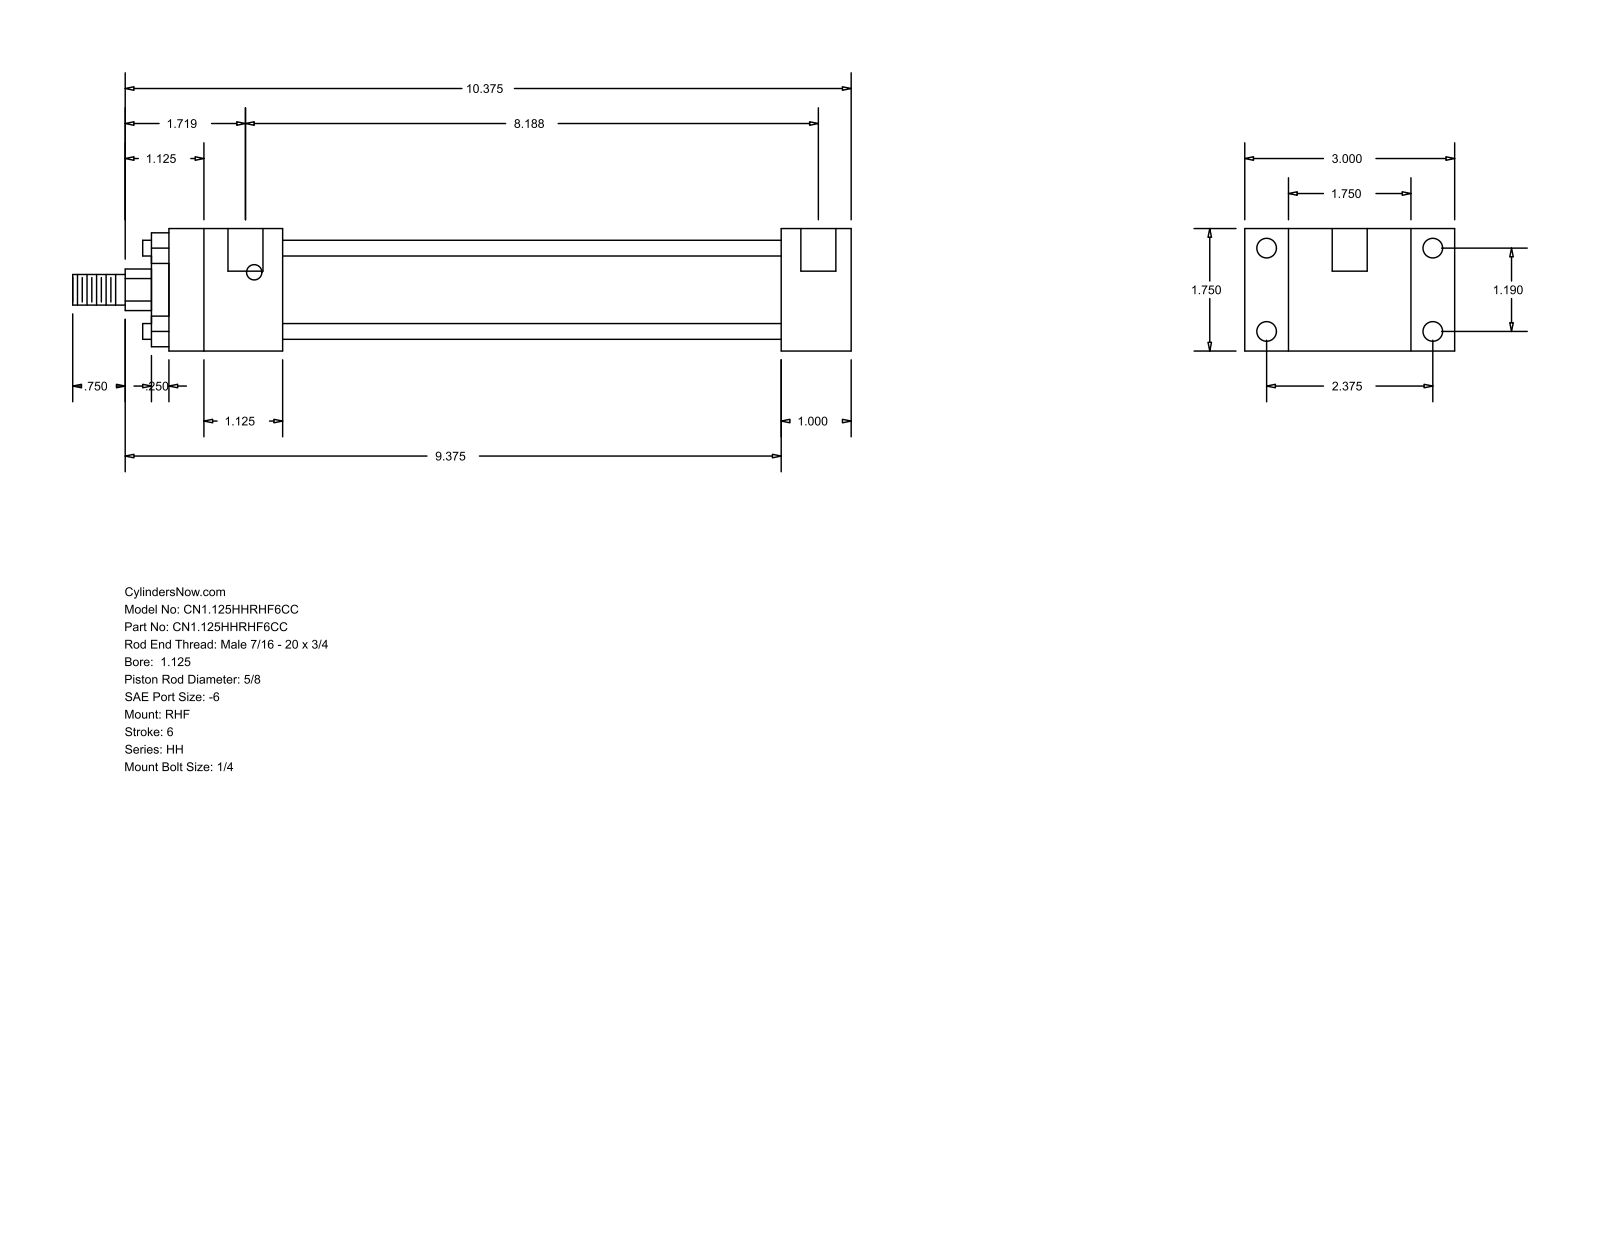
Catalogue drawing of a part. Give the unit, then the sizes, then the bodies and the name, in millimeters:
Units: millimetres
Overall size (bounding box): 282.57 × 76.2 × 44.45
Round holes (diameter × count): ⌀5.56 ×4, ⌀7.14 ×4, ⌀12.7 ×2
Round bosses / shafts (diameter × count): ⌀5.71 ×4, ⌀34.92 ×1, ⌀28.57 ×1, ⌀15.88 ×1, ⌀11.11 ×1
Partial cylindrical surfaces — rounded edges, fillets, slot ends (radius × count): R7.54 ×1
Main face-to-face distances: 44.46, 15.87, 25.4, 60.33, 76.2, 180.97, 206.37, 41.27, 222.24, 247.64
Hole centre spacings: 30.22, 60.32, 67.47, 204.79, 3.17, 207.96
Bodies: 0 solids, 88 faces (60 planar, 28 cylindrical, 0 other)
Part name (STEP PRODUCT): HH_RHF__0112_0.625
STEP written by: GSSL Pune (CONFIG_CONTROL_DESIGN)
